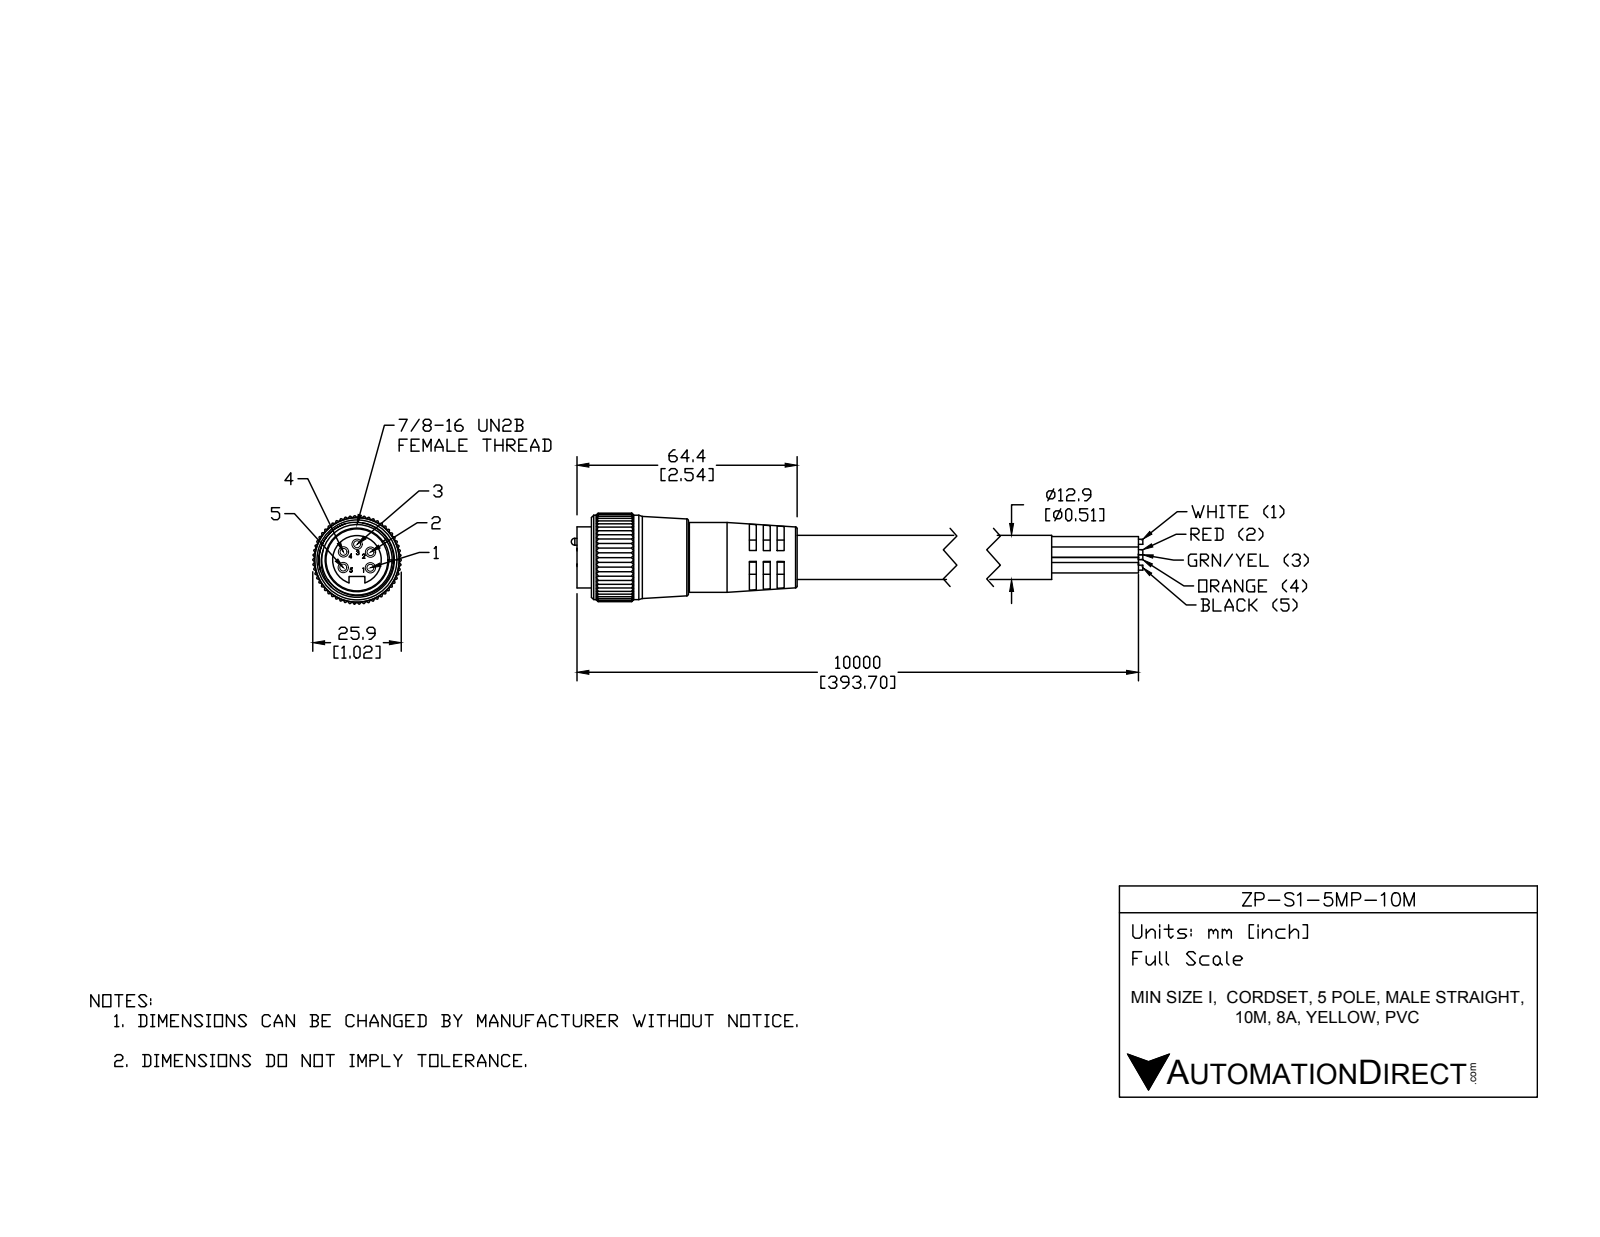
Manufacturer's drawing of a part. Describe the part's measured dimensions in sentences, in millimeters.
The part is named "ZP-S1-5MP-10M". Its 3-D file was written by "SolidWorks 2015 (AUTOMOTIVE_DESIGN)". It is 7 solids with 614 faces: 222 planar, 322 cylindrical and 70 other. Overall it measures 111.14 by 52.91 by 25.84 millimeters. Its volume is 30 938 cubic millimeters and its surface area 13 393 square millimeters. Round holes: 1 of diameter 14.22, 1 of diameter 19.96, 1 of diameter 20.45, 1 of diameter 21. Round bosses or shafts: 5 of diameter 3.05, 5 of diameter 2, 2 of diameter 12.93, 1 of diameter 24.68, 1 of diameter 20.4, 1 of diameter 19.5, 1 of diameter 17.88. Partial cylindrical surfaces (rounded edges, fillets, slot ends): 165 of radius 0.25, 1 of radius 2.29, 1 of radius 5.25, 1 of radius 12.93. The main face-to-face distances are 2, 4.04, 2.04, 6.04, 4.02, 6.06, 8.06, 2.02, 10.07, 8.07.
